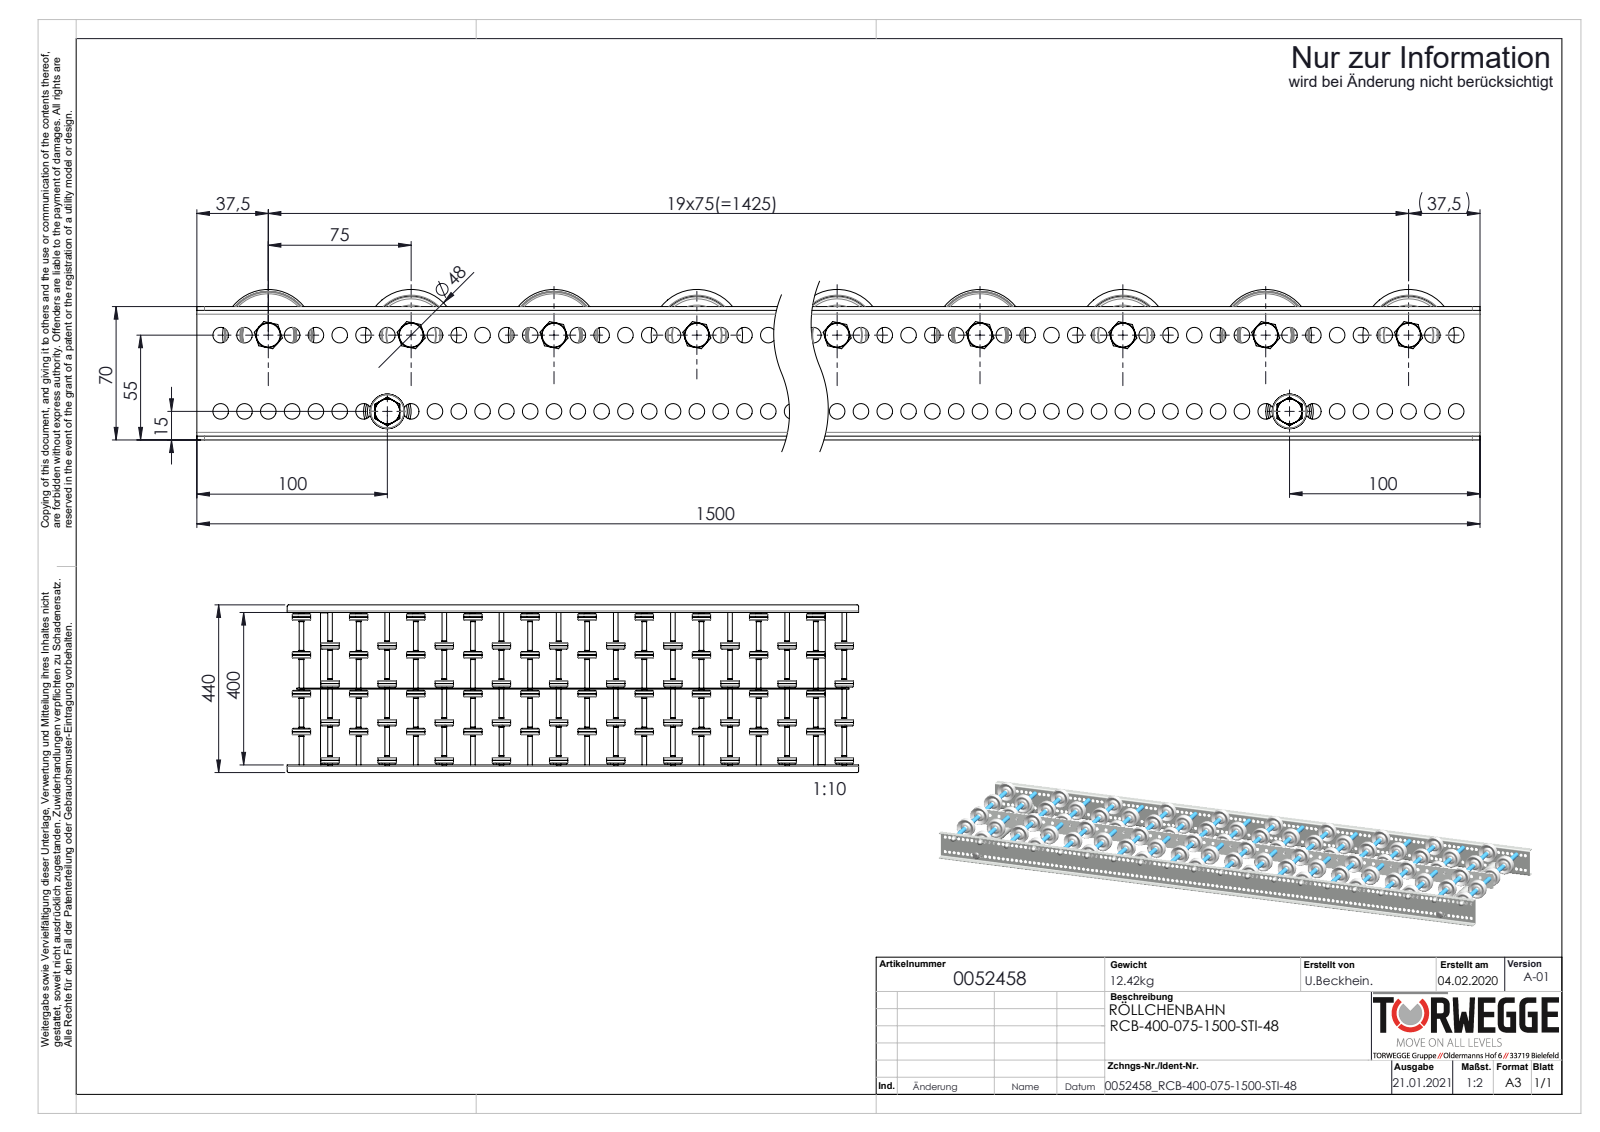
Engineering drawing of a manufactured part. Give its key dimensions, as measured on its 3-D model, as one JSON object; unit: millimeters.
{"part_name": "S100994_Sperrzahnschraube_M08x16-8.8-A2K; Profil_LRB-20x70x20x2_KFG_S100201_U-PROFIL-20-70-20-2-LRB-L=1500; K0011528_2200-48-8; S106837_Gewindestange-M8-KFG_L420 (+6 more)", "step_written_by": "SolidWorks 2020 (AUTOMOTIVE_DESIGN)", "units": "millimeters", "bodies": {"solids": 313, "faces": 9518, "planar": 1926, "cylindrical": 3728, "other": 3864}, "overall_size": [1500, 440, 79], "volume_mm3": 3242000, "surface_area_mm2": 2510000, "round_holes": [[8.2, 238], [8.5, 58], [6.65, 20], [8, 20], [9.65, 20], [15, 20], [41, 20], [6.8, 2], [21, 2]], "round_bosses_or_shafts": [[48, 20], [13, 20], [12.5, 20], [12.4, 20], [12, 20], [11.5, 20], [25, 2], [8, 2]], "partial_cylinders_radius": [[4, 8], [2, 4], [5, 4]], "face_to_face_distances": [2, 201.5, 402, 99.5, 75, 201, 12, 111.5, 87, 186.5], "hole_center_spacings": [12.5, 25, 37.5, 50, 62.5, 75, 87.5, 100]}
